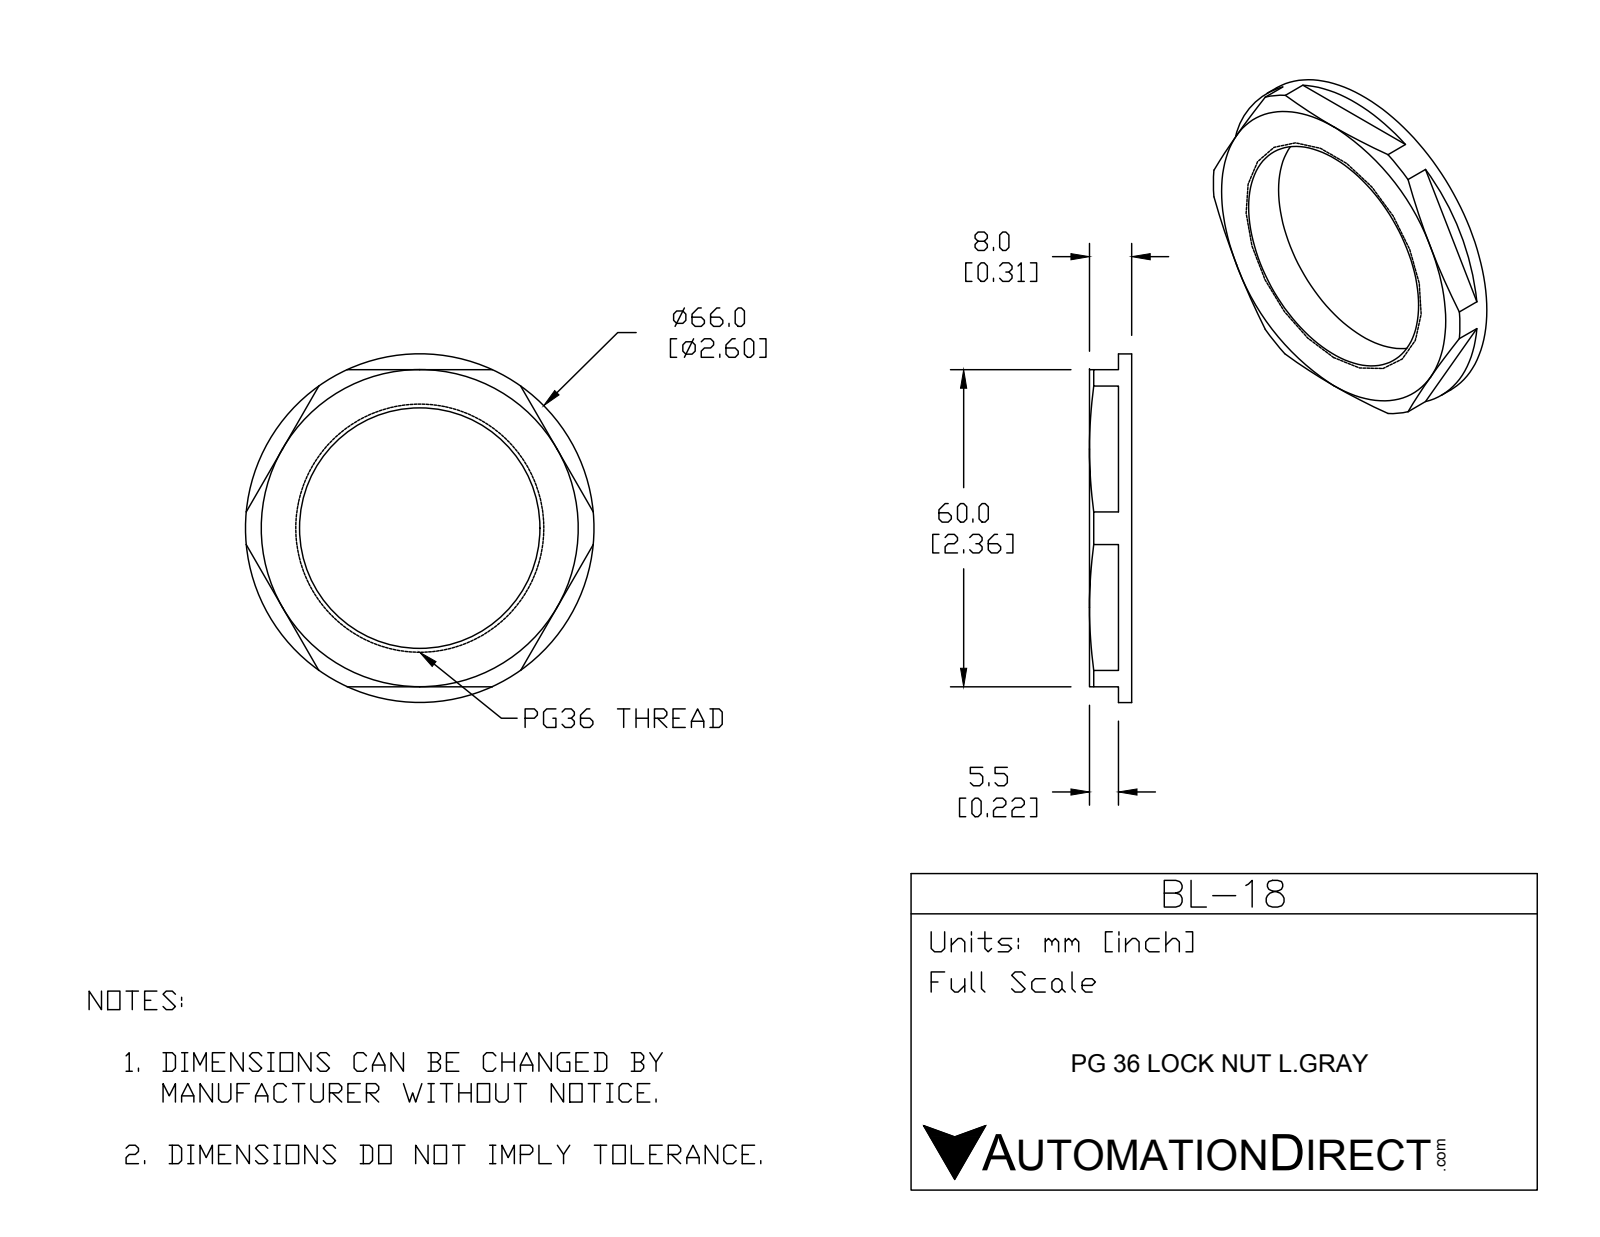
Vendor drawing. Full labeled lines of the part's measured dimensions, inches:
Part name (STEP PRODUCT): BL-18
STEP written by: SolidWorks 2015 (CONFIG_CONTROL_DESIGN)
Units: inches
Bodies: 1 solid, 33 faces (17 planar, 10 cylindrical, 6 other)
Overall size (bounding box): 2.598 × 2.598 × 0.315
Volume: 0.76 in³ · Surface area: 9.77 in²
Round holes (diameter × count): ⌀0.059 ×3, ⌀1.791 ×1
Round bosses / shafts (diameter × count): ⌀2.598 ×1
Main face-to-face distances: 0.315, 2.362, 0.098, 0.217, 0.087, 0.303
Hole centre spacings: 1.242, 2.151, 1.242, 2.152
